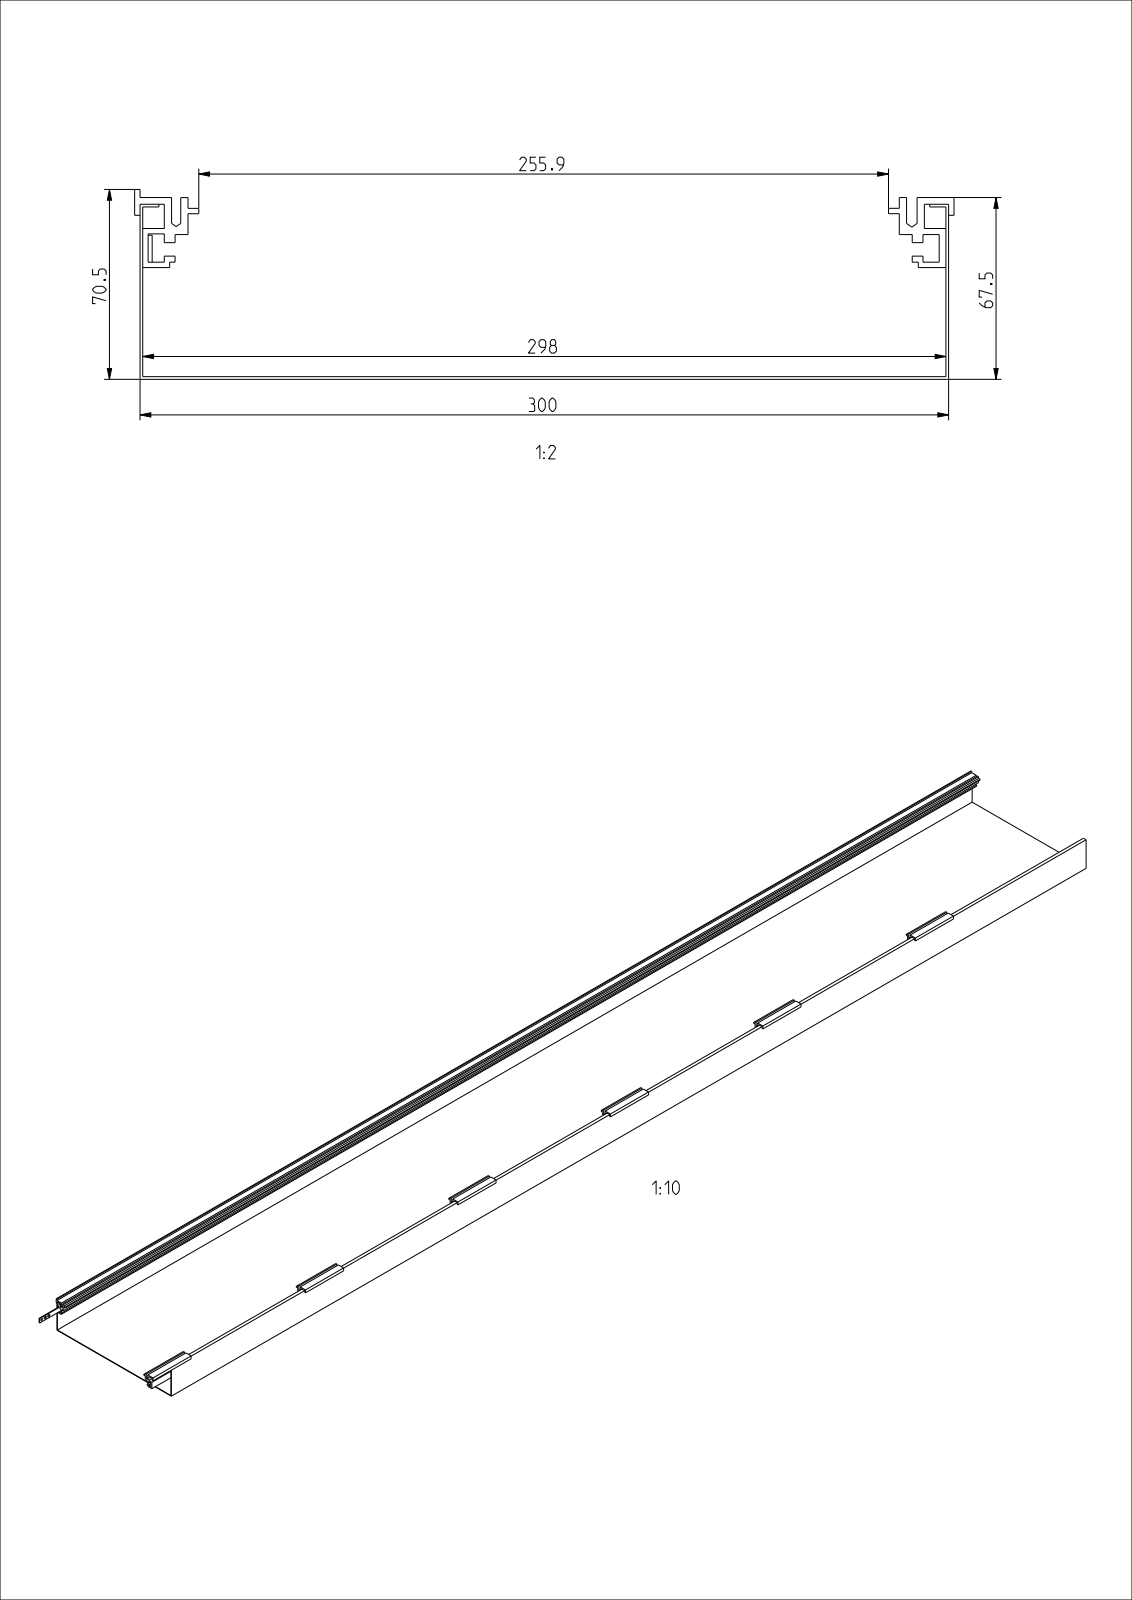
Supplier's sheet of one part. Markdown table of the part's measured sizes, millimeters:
| quantity | value |
| --- | --- |
| part name | AKU3000701_WANNE_3; AKU_SEITENPROFIL_APA_K24_6; ZES_VK180_KUN_3; AKU_SEITENPROFIL_APA_O01_4 (+2 more) |
| STEP written by | CREO PARAMETRIC BY PTC INC, 2022281 (AUTOMOTIVE_DESIGN) |
| units | millimeters |
| bodies | 9 solids, 265 faces (253 planar, 12 cylindrical, 0 other) |
| overall size | 2450 × 304 × 70.5 |
| volume | 1 701 000 mm³ |
| surface area | 2 662 000 mm² |
| round holes (diameter × count) | 5.5 × 4, 4.2 × 2 |
| main face-to-face distances | 1, 299, 298, 300, 2, 64, 8, 3, 9, 65 |
| hole center spacings | 9.25, 66.5, 18.5, 57.25, 75.75, 48, 85 |
